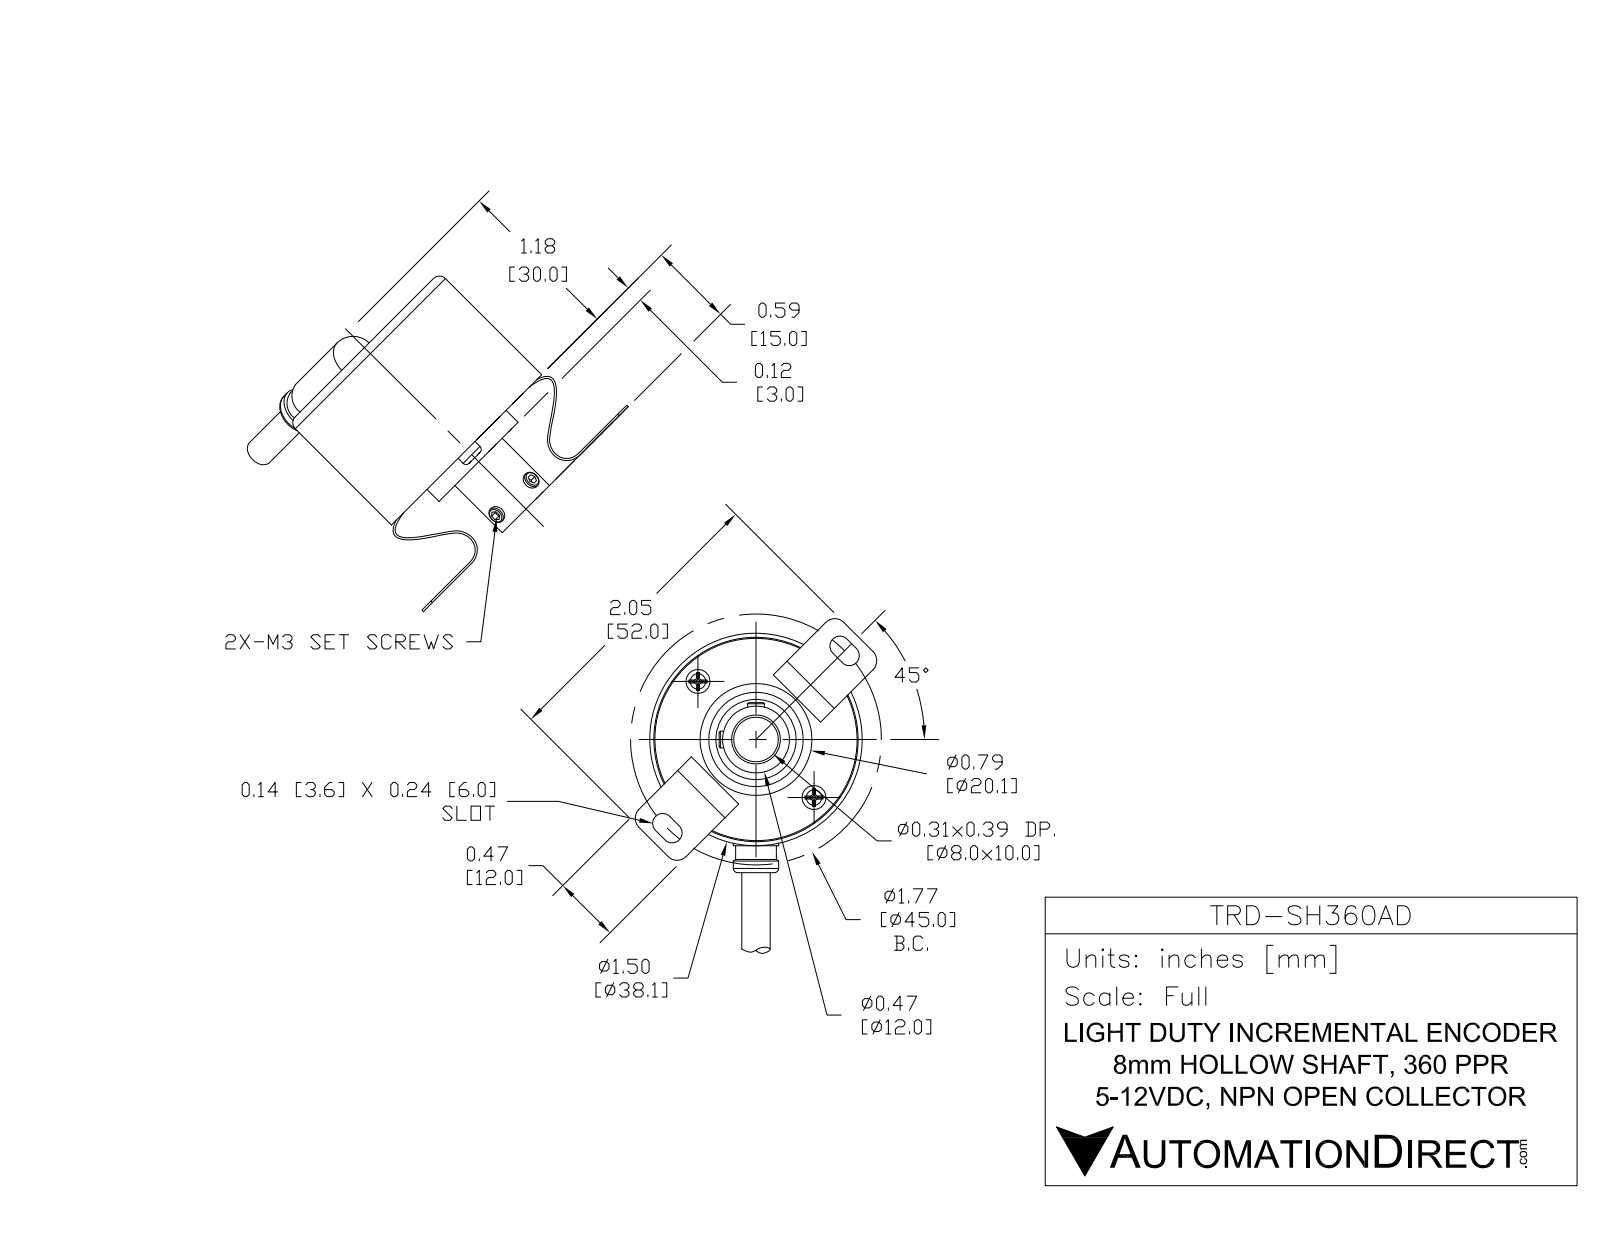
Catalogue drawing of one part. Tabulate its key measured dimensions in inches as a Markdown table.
| quantity | value |
| --- | --- |
| part name | TRD-SH-360AD |
| STEP written by | SolidWorks 2016 (AUTOMOTIVE_DESIGN) |
| units | inches |
| bodies | 11 solids, 322 faces (169 planar, 101 cylindrical, 52 other) |
| overall size | 3.952 × 1.772 × 1.684 |
| volume | 2.043 in³ |
| surface area | 17.32 in² |
| round holes (diameter × count) | 0.126 × 5, 0.098 × 2, 0.315 × 1, 0.791 × 1 |
| round bosses / shafts (diameter × count) | 0.118 × 5, 1.496 × 1, 0.787 × 1, 0.591 × 1, 0.472 × 1, 0.299 × 1, 0.197 × 1, 0.134 × 1 |
| partial cylindrical surfaces (radius × count) | 0.039 × 6, 0.118 × 5, 0.03 × 4, 0.071 × 4, 0.087 × 4, 0.098 × 4, 0.031 × 2, 0.146 × 2 |
| main face-to-face distances | 1.024, 0.579, 1.035, 0.591, 1.614, 1.602, 0.567, 0.118, 1.142, 0.106 |
| hole center spacings | 0.551, 0.78, 0.955, 0.285, 0.285, 0.954, 1.065, 1.065 |
